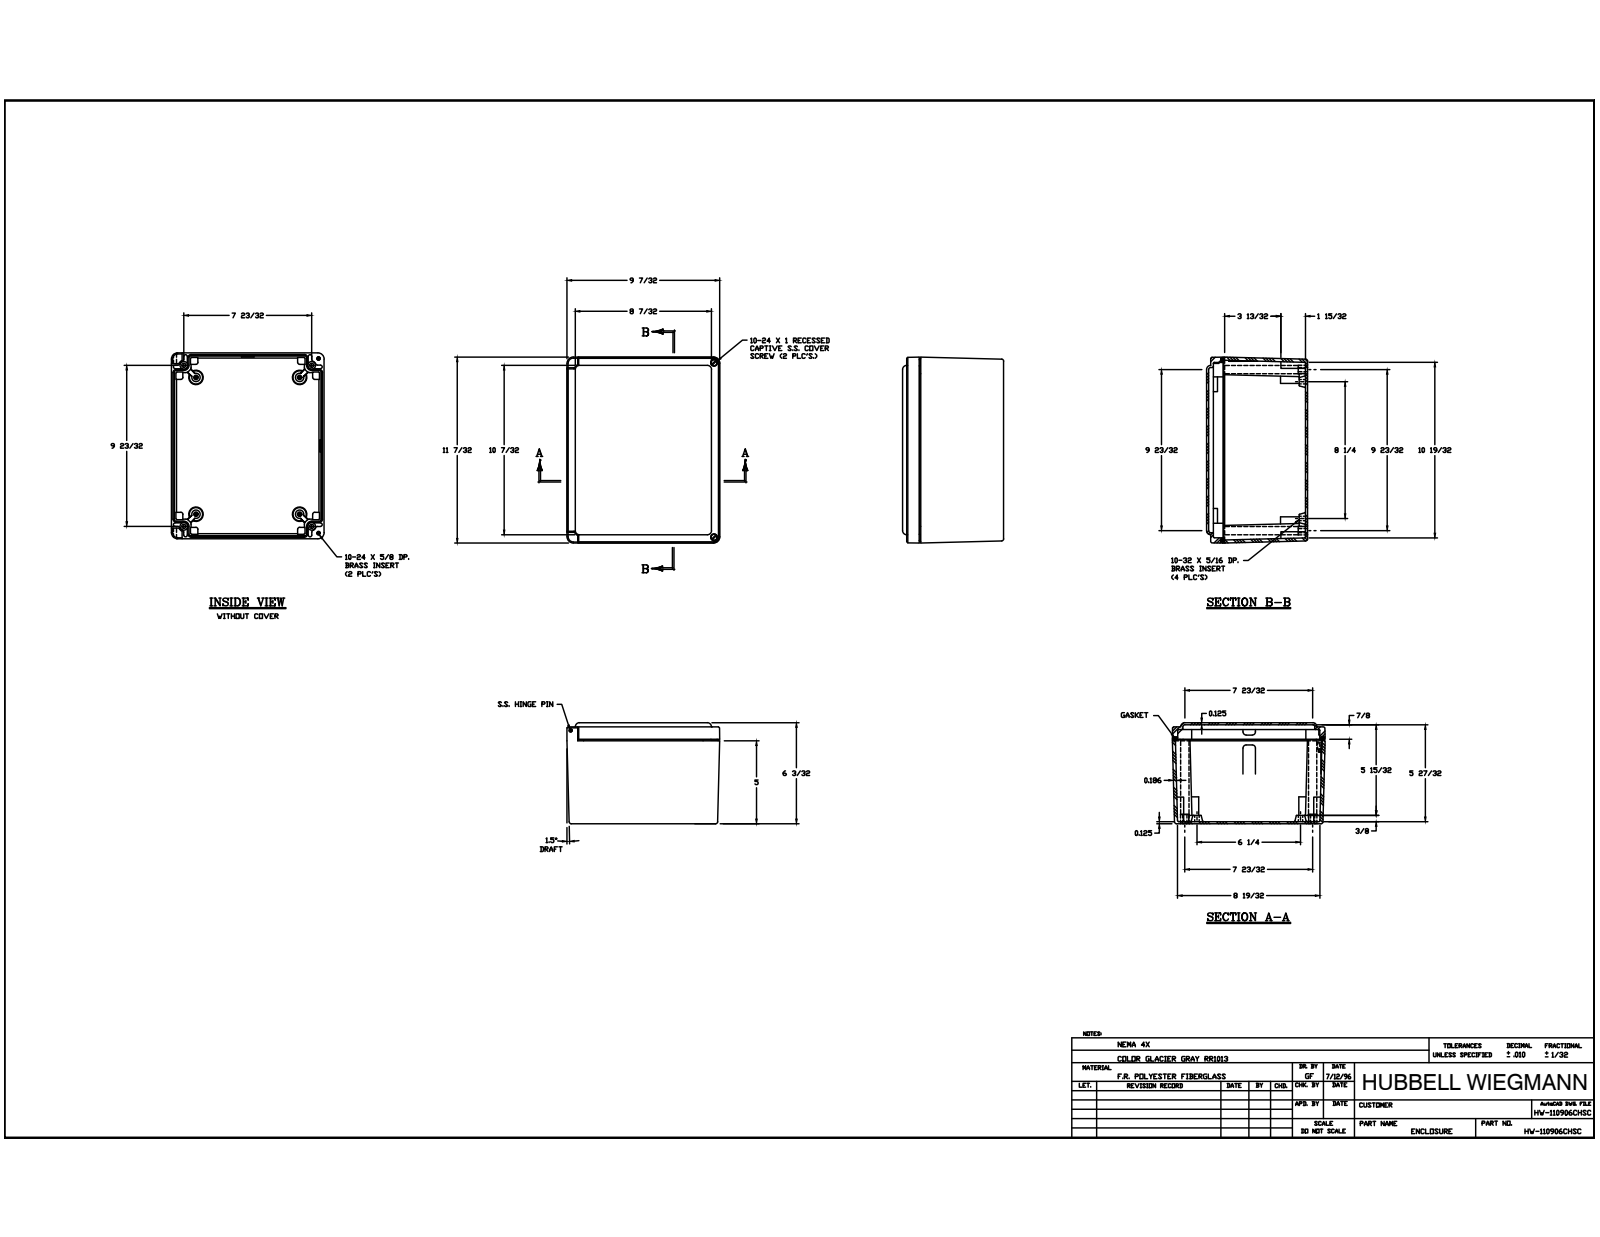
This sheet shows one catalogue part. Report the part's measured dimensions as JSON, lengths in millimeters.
{"part_name": "WP1109HWBOX; 0.3125-18 X 0.563 DP BRASS INSERT; 10-32 X0.3125 DP BRASS INSERT; 10-24 X 0.625 DP BRASS INSERT (+8 more)", "step_written_by": "Autodesk Inventor 2014 (AUTOMOTIVE_DESIGN)", "units": "millimeters", "bodies": {"solids": 23, "faces": 1024, "planar": 398, "cylindrical": 294, "other": 332}, "overall_size": [285.26, 234.46, 154.78], "volume_mm3": 1366000, "surface_area_mm2": 623655, "round_holes": [[7.14, 6], [3.96, 4], [7.94, 4], [13.49, 4], [2.44, 2], [3.68, 2], [3.97, 2], [4.76, 2], [4.83, 2], [5.56, 2], [5.84, 2], [7.1, 2]], "round_bosses_or_shafts": [[9.52, 2], [9.24, 2], [5.94, 2], [4.86, 2], [2.42, 2], [9.42, 1], [4.52, 1], [2.24, 1]], "partial_cylinders_radius": [[0.79, 60], [3.17, 38], [1.59, 29], [0.25, 8], [1.5, 8], [4.78, 8], [6.35, 8], [9.53, 8]], "face_to_face_distances": [3.17, 151.61, 4.72, 154.78, 148.44, 3.18, 6.35, 148.43, 145.26, 19.05], "hole_center_spacings": [26.39, 178.68, 229.26, 289.46, 0.32, 0.34, 13.42, 14.26]}
